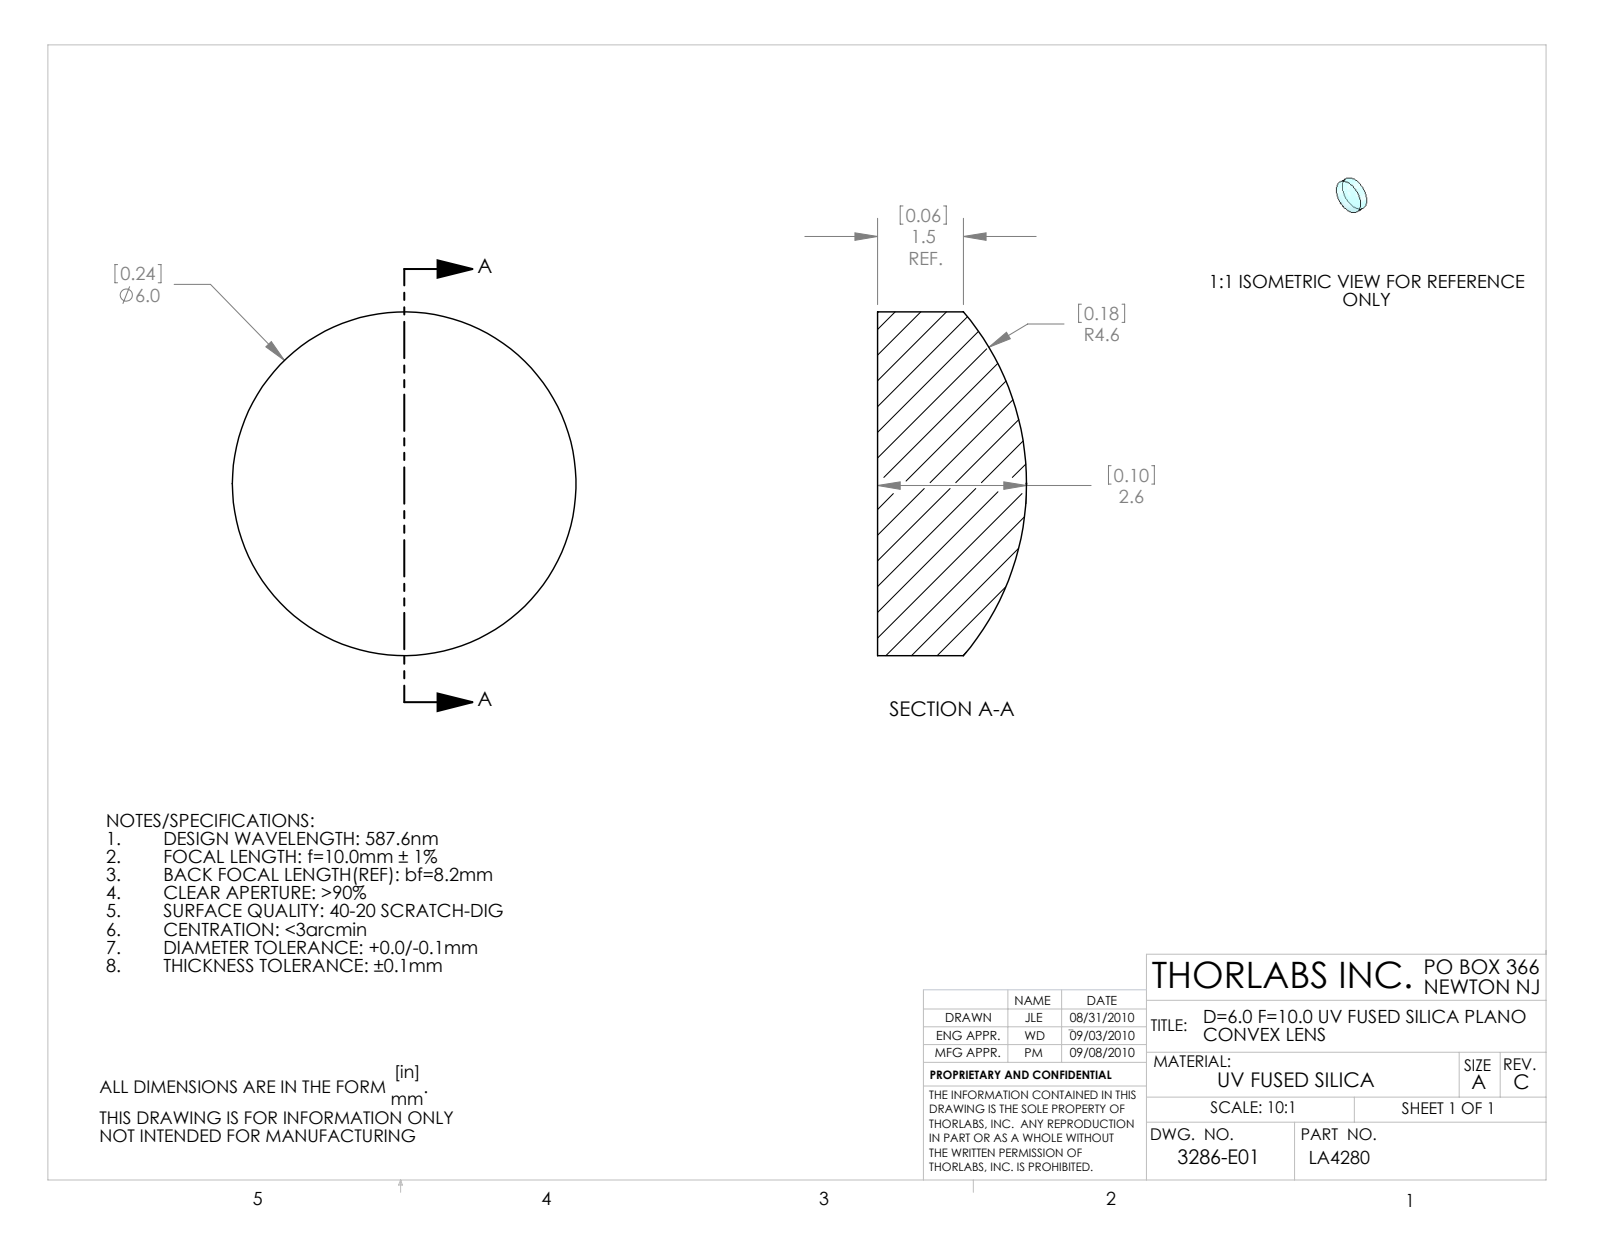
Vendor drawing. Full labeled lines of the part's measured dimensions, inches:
Part name (STEP PRODUCT): 3286-E0W
STEP written by: SolidWorks 2009 (AUTOMOTIVE_DESIGN)
Units: inches
Bodies: 1 solid, 5 faces (1 planar, 2 cylindrical, 2 other)
Overall size (bounding box): 0.236 × 0.236 × 0.102
Volume: 0.004 in³ · Surface area: 0.137 in²
Round bosses / shafts (diameter × count): ⌀0.236 ×1
